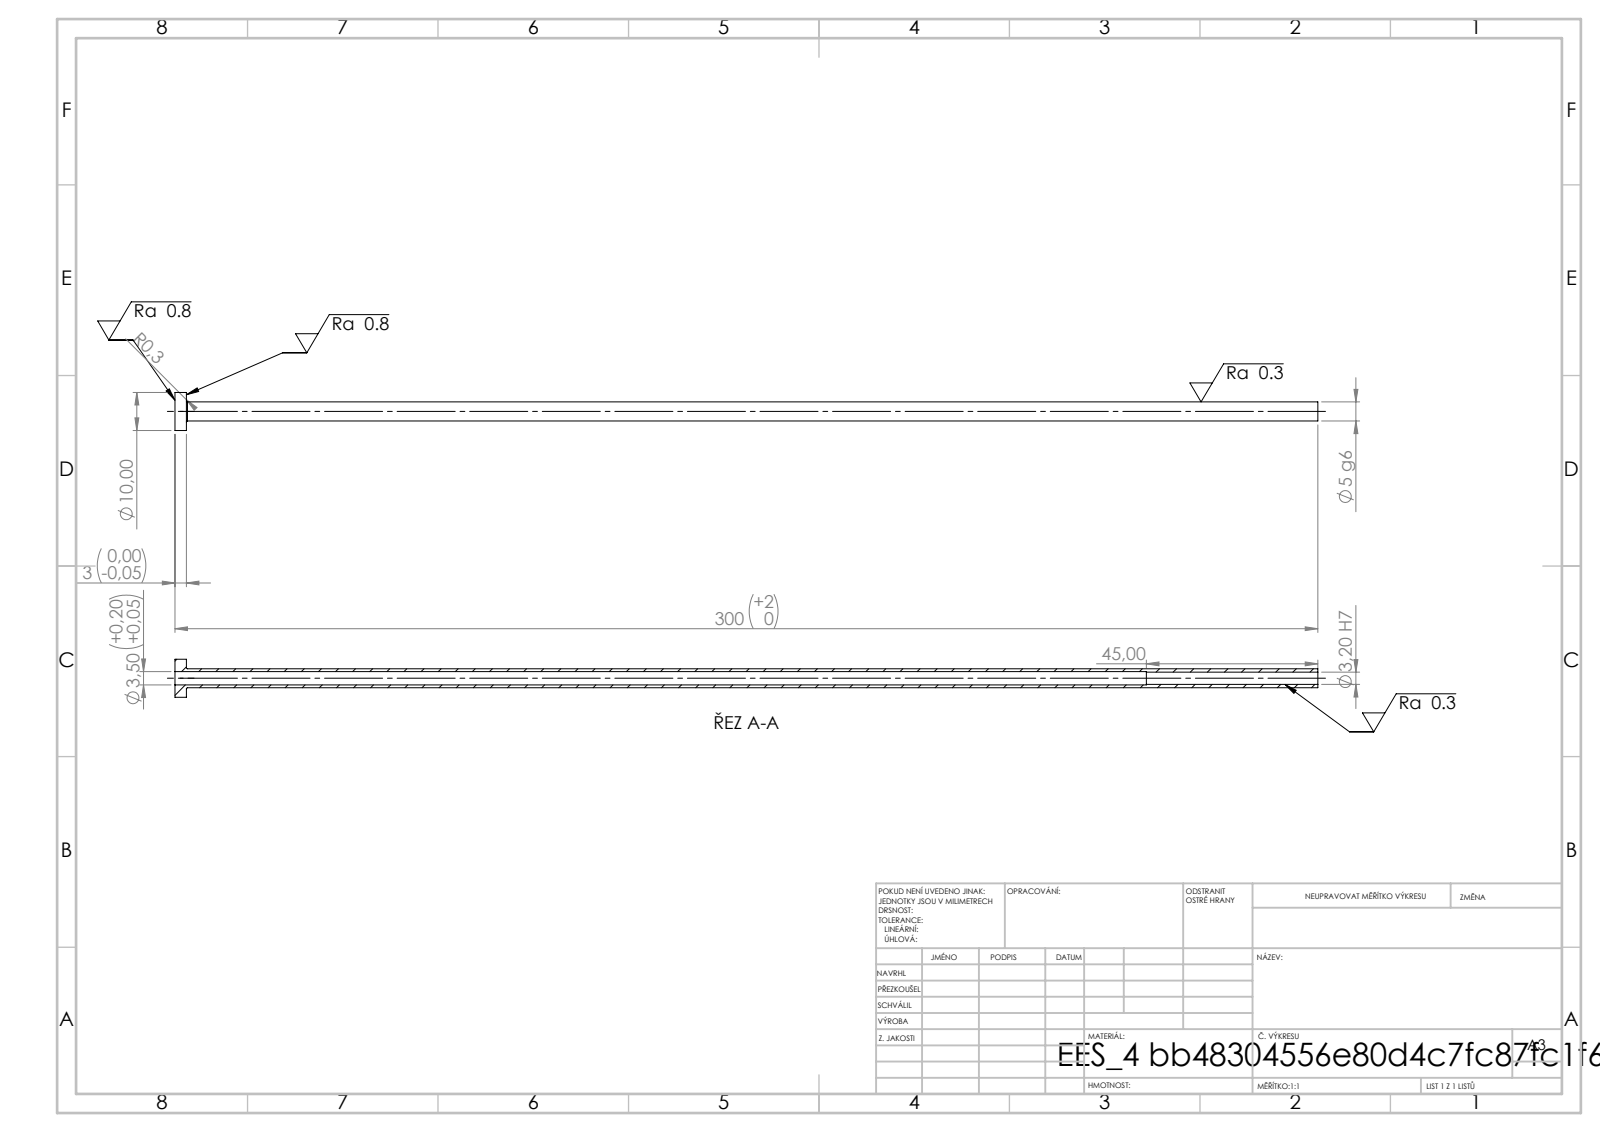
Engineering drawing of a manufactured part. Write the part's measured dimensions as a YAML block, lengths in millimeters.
step_written_by: "SolidWorks 2019 (CONFIG_CONTROL_DESIGN)"
units: millimeters
bodies: {solids: 1, faces: 14, planar: 4, cylindrical: 8, other: 2}
overall_size: [300, 10, 10]
volume: 3252
surface_area: 8155
round_holes:
  - {diameter: 3.2, count: 1}
  - {diameter: 3.5, count: 1}
round_bosses_or_shafts:
  - {diameter: 10, count: 1}
  - {diameter: 5, count: 1}
face_to_face_distances: [3, 300, 297, 255, 252, 45]
